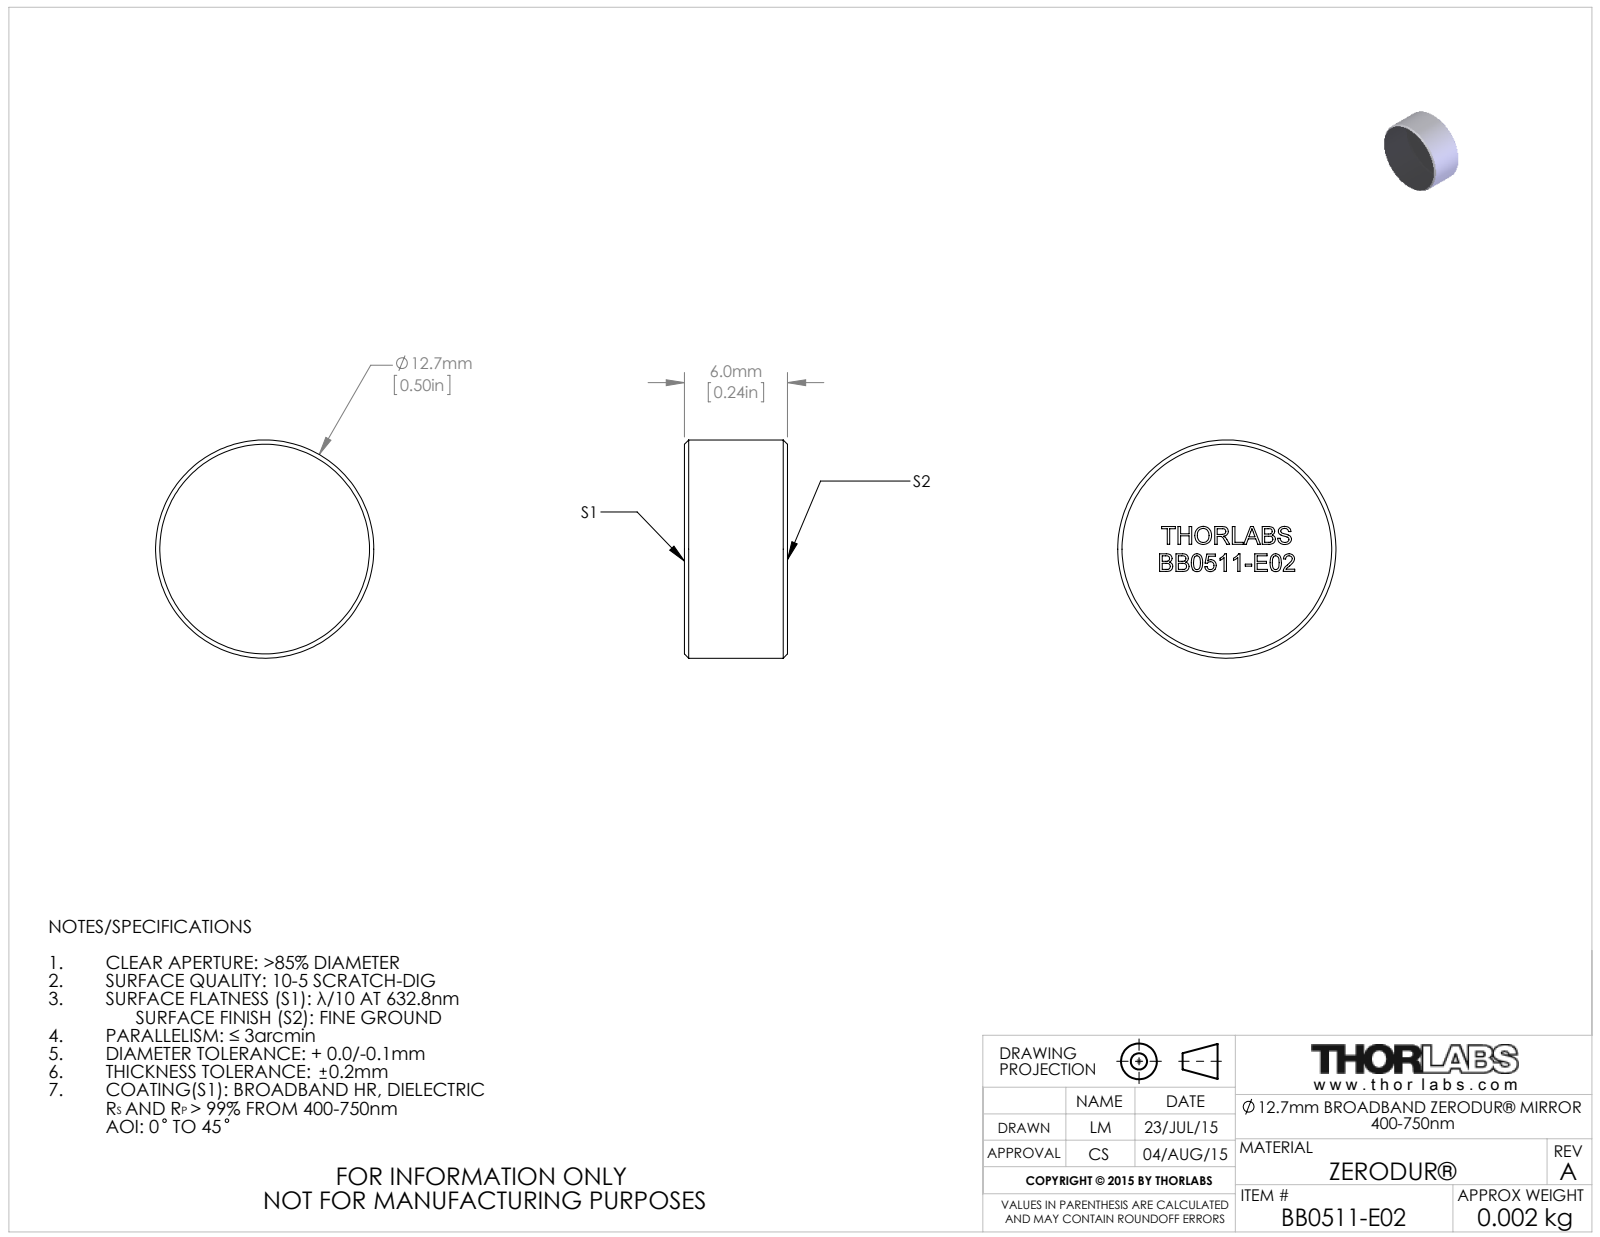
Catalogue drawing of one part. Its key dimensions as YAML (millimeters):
part_name: "TTN045133-E0W"
step_written_by: "SolidWorks 2014 (CONFIG_CONTROL_DESIGN)"
units: millimeters
bodies: {solids: 1, faces: 255, planar: 145, cylindrical: 2, other: 108}
overall_size: [12.7, 12.7, 6]
volume: 758
surface_area: 481
round_bosses_or_shafts:
  - {diameter: 12.7, count: 1}
face_to_face_distances: [6, 1.58, 0.44, 0.79, 0.91, 1.03, 1.28, 1.46, 2.02, 0.67]
